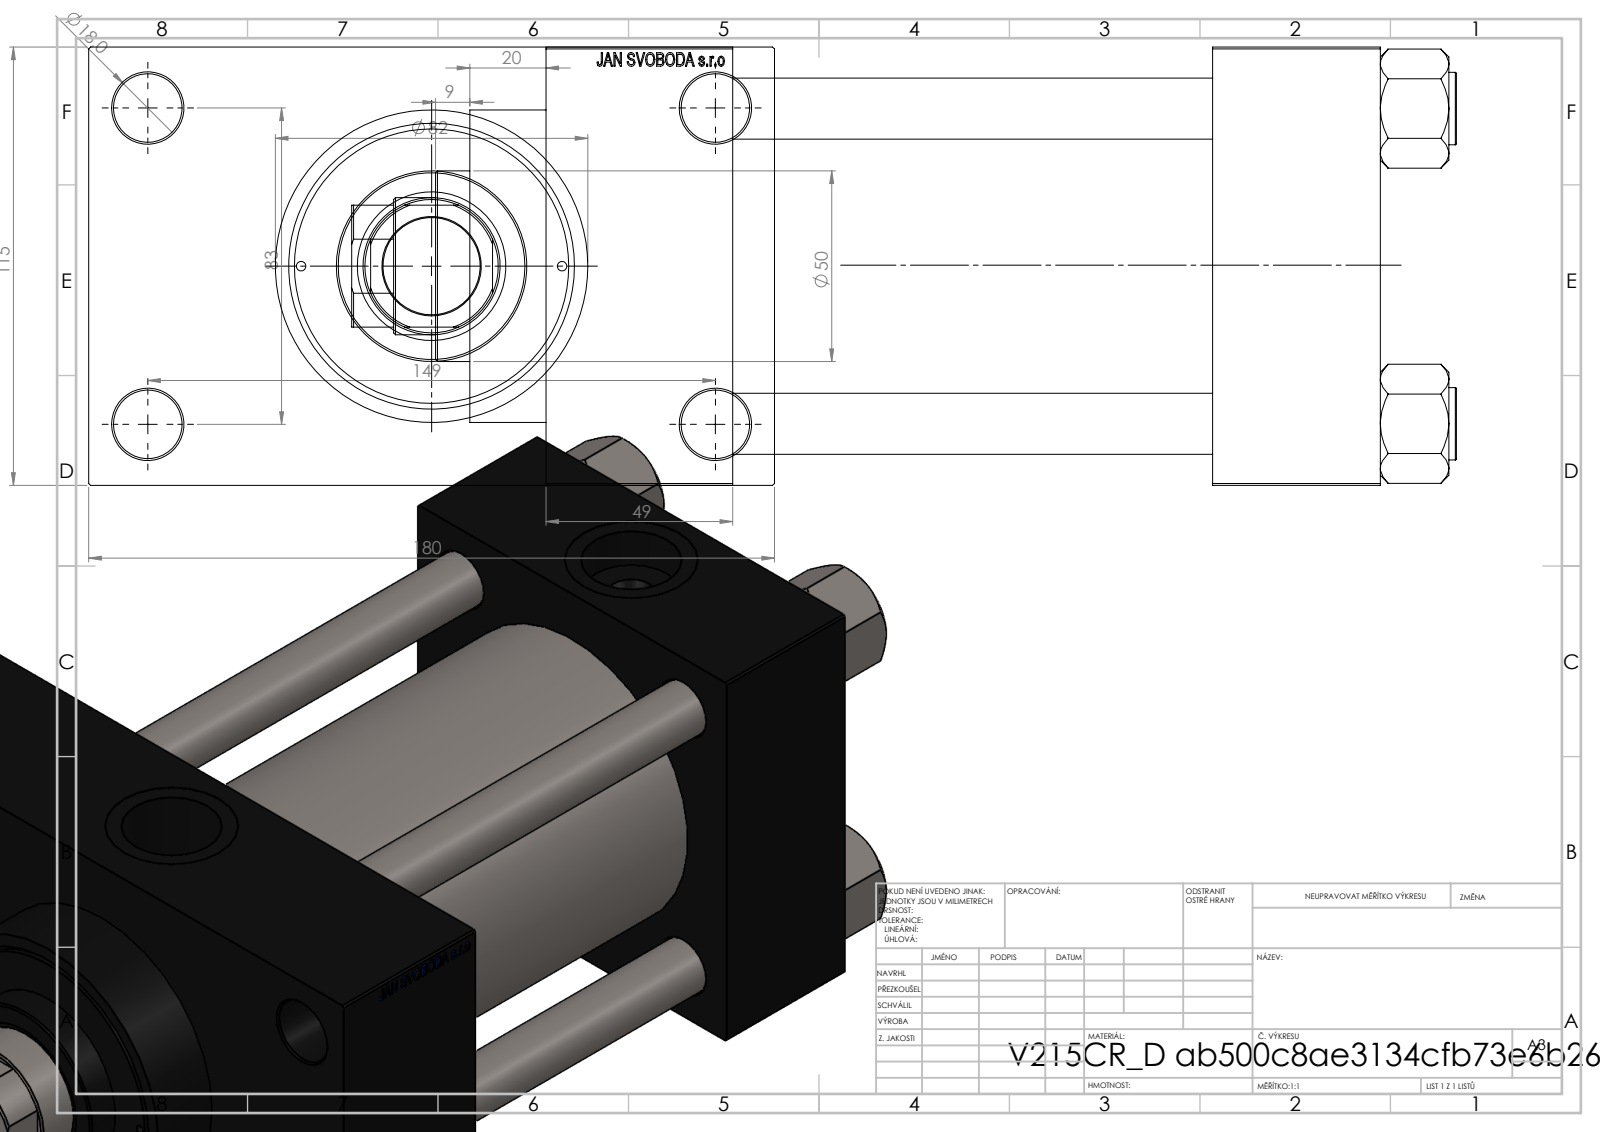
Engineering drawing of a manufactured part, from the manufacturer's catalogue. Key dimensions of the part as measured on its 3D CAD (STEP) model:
Part name (STEP PRODUCT): V215CR_VCP_D; NUT_M5_D; V215CR_D_Body; V215CR_D_TYCINKA (+1 more)
STEP written by: SolidWorks 2019 (CONFIG_CONTROL_DESIGN)
Units: millimetres
Bodies: 11 solids, 1160 faces (547 planar, 93 cylindrical, 520 other)
Overall size (bounding box): 290 × 180 × 115
Volume: 2 153 000 mm³ · Surface area: 343 926 mm²
Round holes (diameter × count): ⌀16 ×4, ⌀18 ×4, ⌀2.5 ×2, ⌀7 ×2, ⌀26.44 ×2, ⌀35 ×2, ⌀25.5 ×1, ⌀36 ×1, ⌀39 ×1, ⌀61 ×1, ⌀72 ×1, ⌀80 ×1
Round bosses / shafts (diameter × count): ⌀19 ×4, ⌀86 ×1, ⌀82 ×1, ⌀50 ×1
Partial cylindrical surfaces — rounded edges, fillets, slot ends (radius × count): R17.5 ×1
Main face-to-face distances: 115, 126, 175, 49, 170, 44, 219, 32.5, 147.5, 180
Hole centre spacings: 33.15, 41.96, 57.81, 58.48, 82.7, 85.28, 86.17, 89.24
